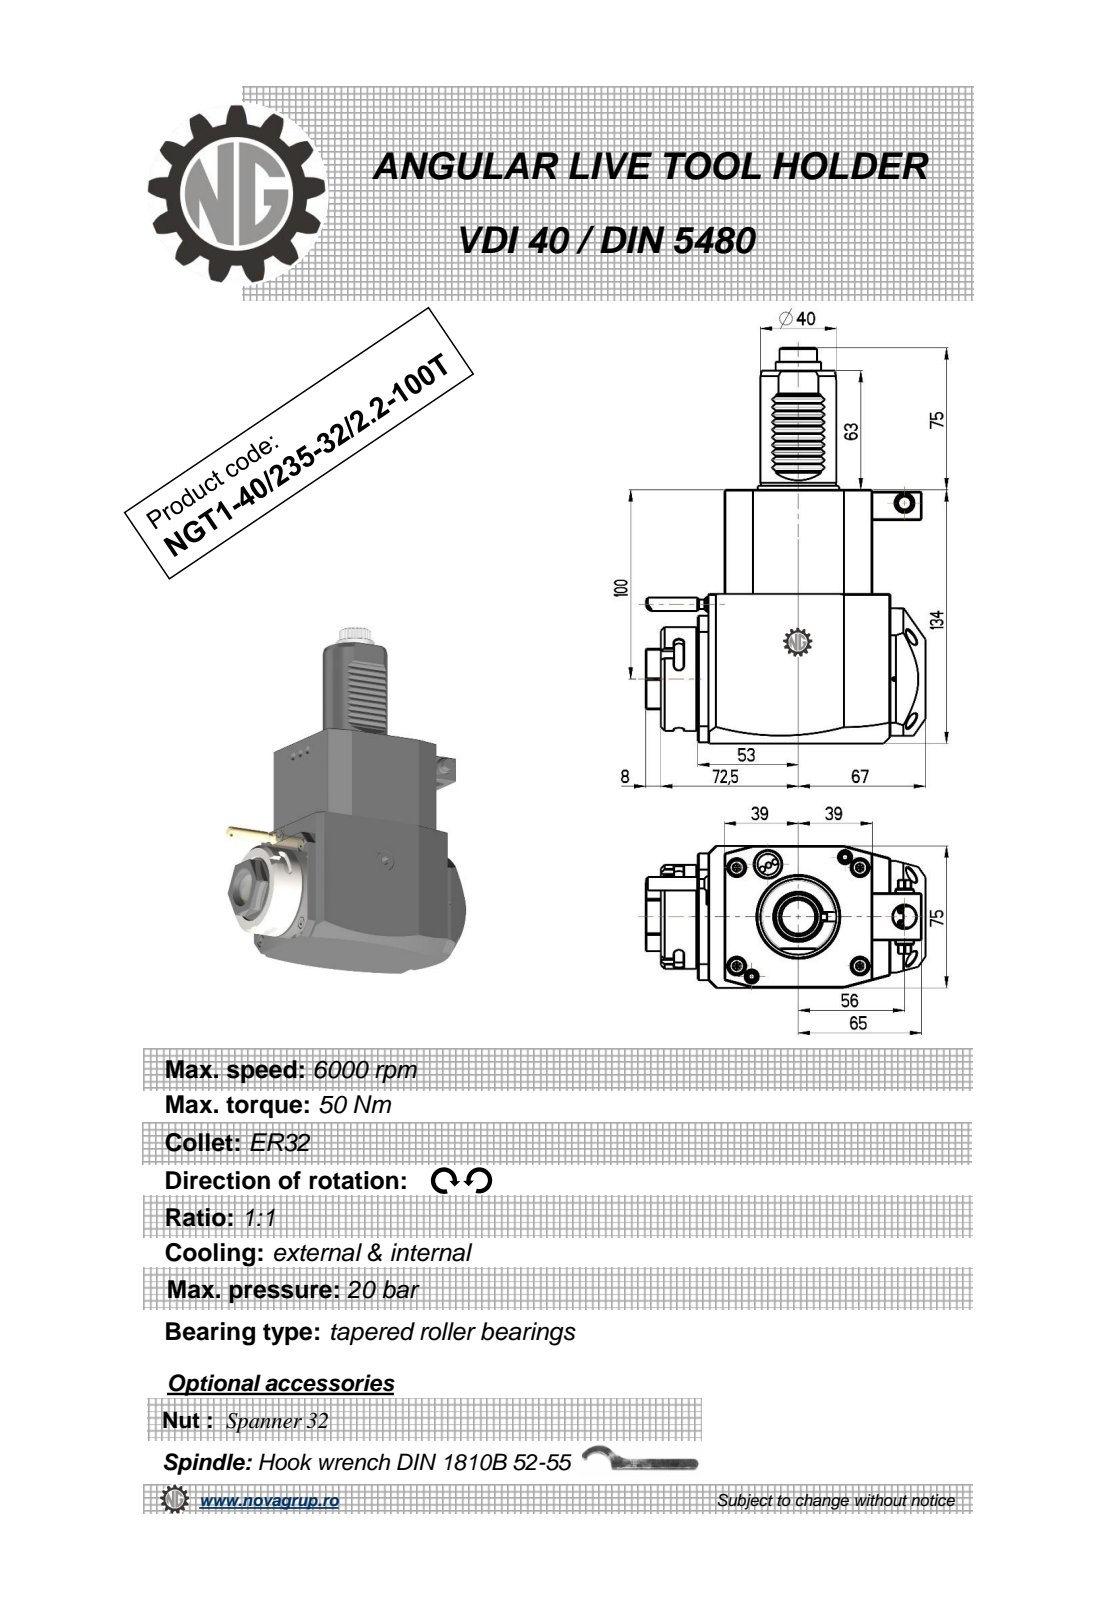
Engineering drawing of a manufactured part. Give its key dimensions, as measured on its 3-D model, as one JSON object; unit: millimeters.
{"part_name": "NGT1_40_235_32_1_2_100T", "step_written_by": "PRO/ENGINEER BY PARAMETRIC TECHNOLOGY CORPORATION, 2010280 (CONFIG_CONTROL_DESIGN)", "units": "millimeters", "bodies": {"solids": 1, "faces": 458, "planar": 192, "cylindrical": 172, "other": 94}, "overall_size": [209, 147.5, 75], "volume_mm3": 1080000, "surface_area_mm2": 77887, "round_holes": [[2.5, 1], [3, 1], [9.5, 1], [12, 1], [23, 1]], "round_bosses_or_shafts": [[8, 2], [55, 1], [48, 1], [40, 1], [24, 1], [10, 1], [7, 1], [5, 1]], "partial_cylinders_radius": [[2.08, 48], [0.3, 10], [2.5, 6], [180, 2], [3.85, 1], [4.25, 1], [9.08, 1], [9.92, 1]], "face_to_face_distances": [75, 134, 78, 14, 92, 79, 25, 84.88, 19.5, 33.5], "hole_center_spacings": [43.2, 54.87, 91.5]}
